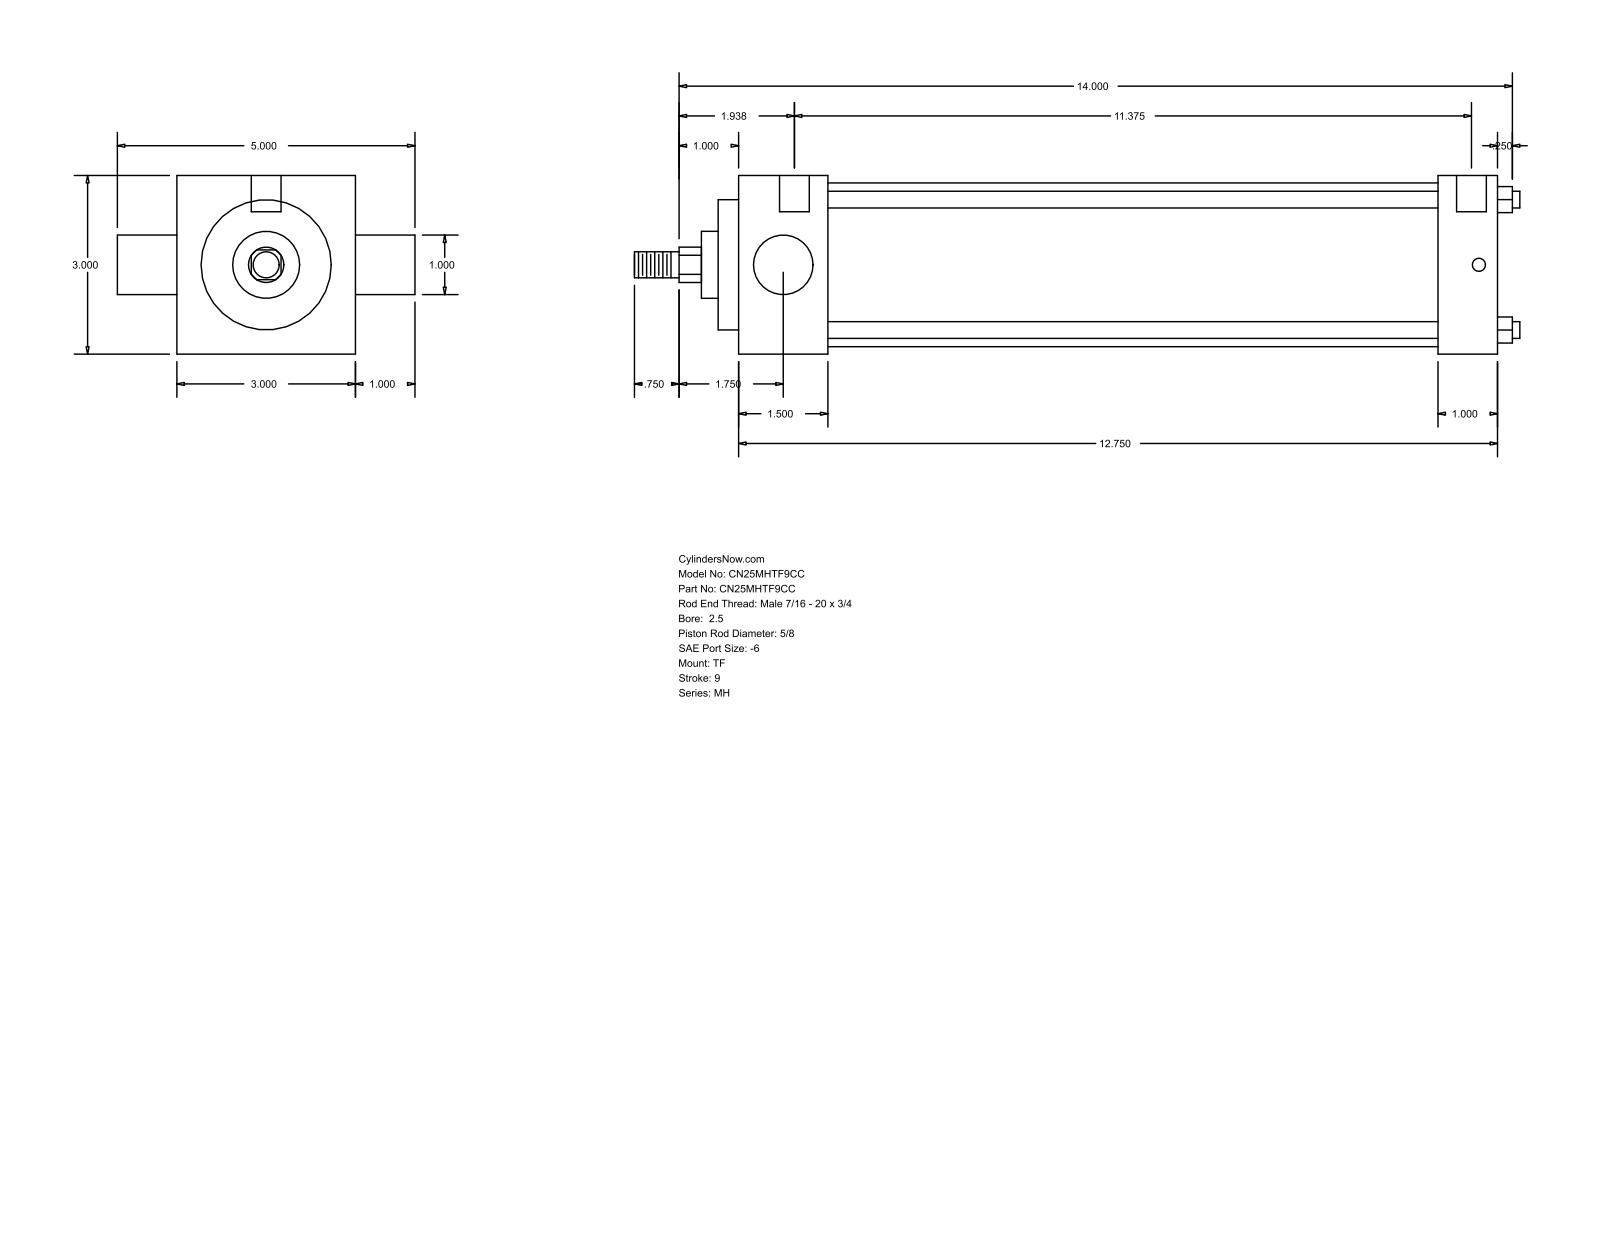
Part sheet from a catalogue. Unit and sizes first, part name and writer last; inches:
Units: inches
Overall size (bounding box): 14.875 × 5 × 3
Round holes (diameter × count): ⌀0.219 ×3, ⌀0.5 ×2
Round bosses / shafts (diameter × count): ⌀0.281 ×4, ⌀2.75 ×1, ⌀2.187 ×1, ⌀1.125 ×1, ⌀1 ×1, ⌀0.625 ×1, ⌀0.437 ×1
Partial cylindrical surfaces — rounded edges, fillets, slot ends (radius × count): R0.297 ×1
Main face-to-face distances: 3, 12.75, 1, 1.5, 11.25, 11.75, 10.25, 0.344, 1.844, 12.094
Hole centre spacings: 0.125, 0.187, 11.375, 11.5, 11.563, 11.687
Bodies: 0 solids, 86 faces (61 planar, 25 cylindrical, 0 other)
Part name (STEP PRODUCT): MH_TF__0250_0.625
STEP written by: GSSL Pune (CONFIG_CONTROL_DESIGN)
